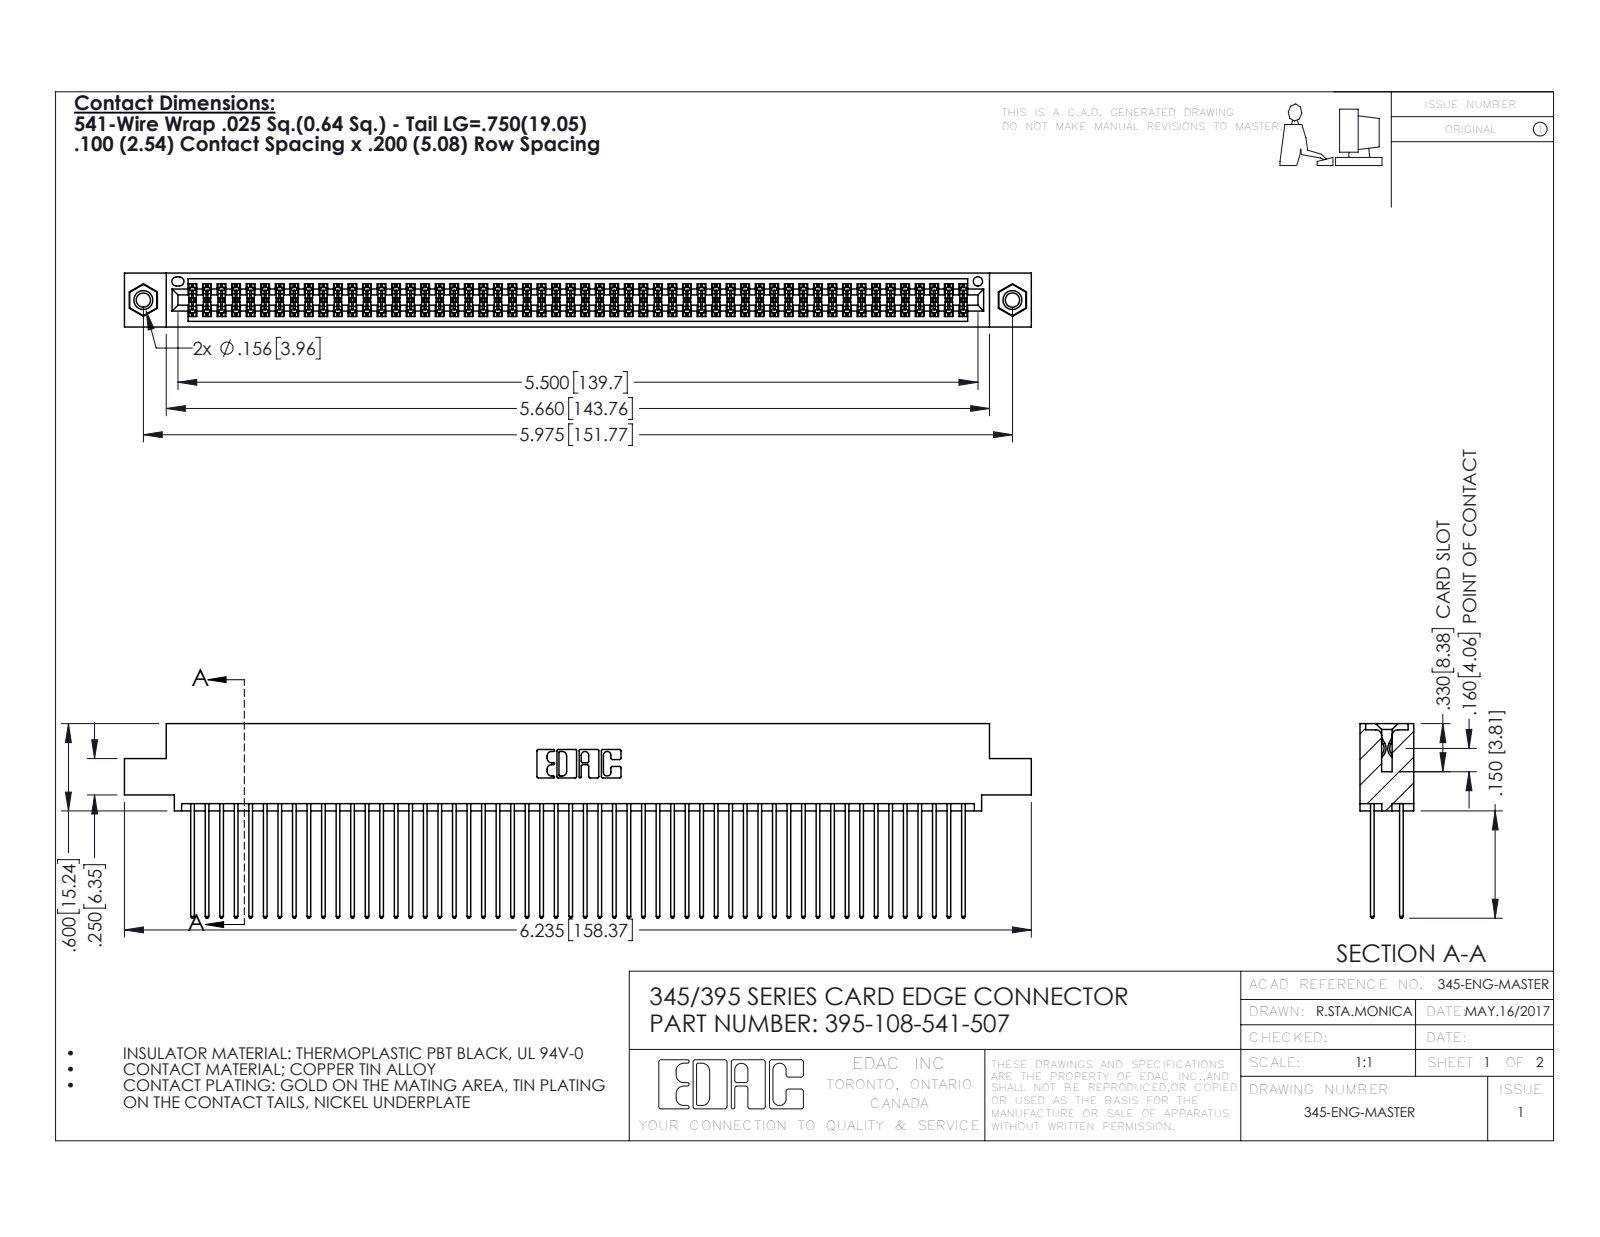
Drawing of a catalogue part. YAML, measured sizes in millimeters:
part_name: "395-108-541-507; 345-292-001_345-293-141; 345-250-001_345-250-005-103; 345 Part_0.110 Offset - 0.156 Dia-TI"
step_written_by: "SolidWorks 2016 (CONFIG_CONTROL_DESIGN)"
units: millimeters
bodies: {solids: 111, faces: 5590, planar: 3680, cylindrical: 1894, other: 16}
overall_size: [158.4, 34, 9.4]
volume: 16000
surface_area: 26960
round_holes:
  - {diameter: 2.5, count: 2}
  - {diameter: 3.2, count: 2}
  - {diameter: 4, count: 2}
  - {diameter: 1.6, count: 1}
round_bosses_or_shafts:
  - {diameter: 3.9, count: 2}
partial_cylinders:
  - {radius: 0.2, count: 162}
  - {radius: 0.3, count: 108}
  - {radius: 0.3, count: 22}
  - {radius: 0.2, count: 6}
  - {radius: 0.8, count: 6}
  - {radius: 0.7, count: 3}
  - {radius: 0.4, count: 2}
  - {radius: 0.5, count: 2}
face_to_face_distances: [1.8, 7.6, 5.1, 2.5, 6.9, 0.6, 5.7, 9.4, 4.4, 3.8]
hole_center_spacings: [6.9, 145.8, 151.8]
